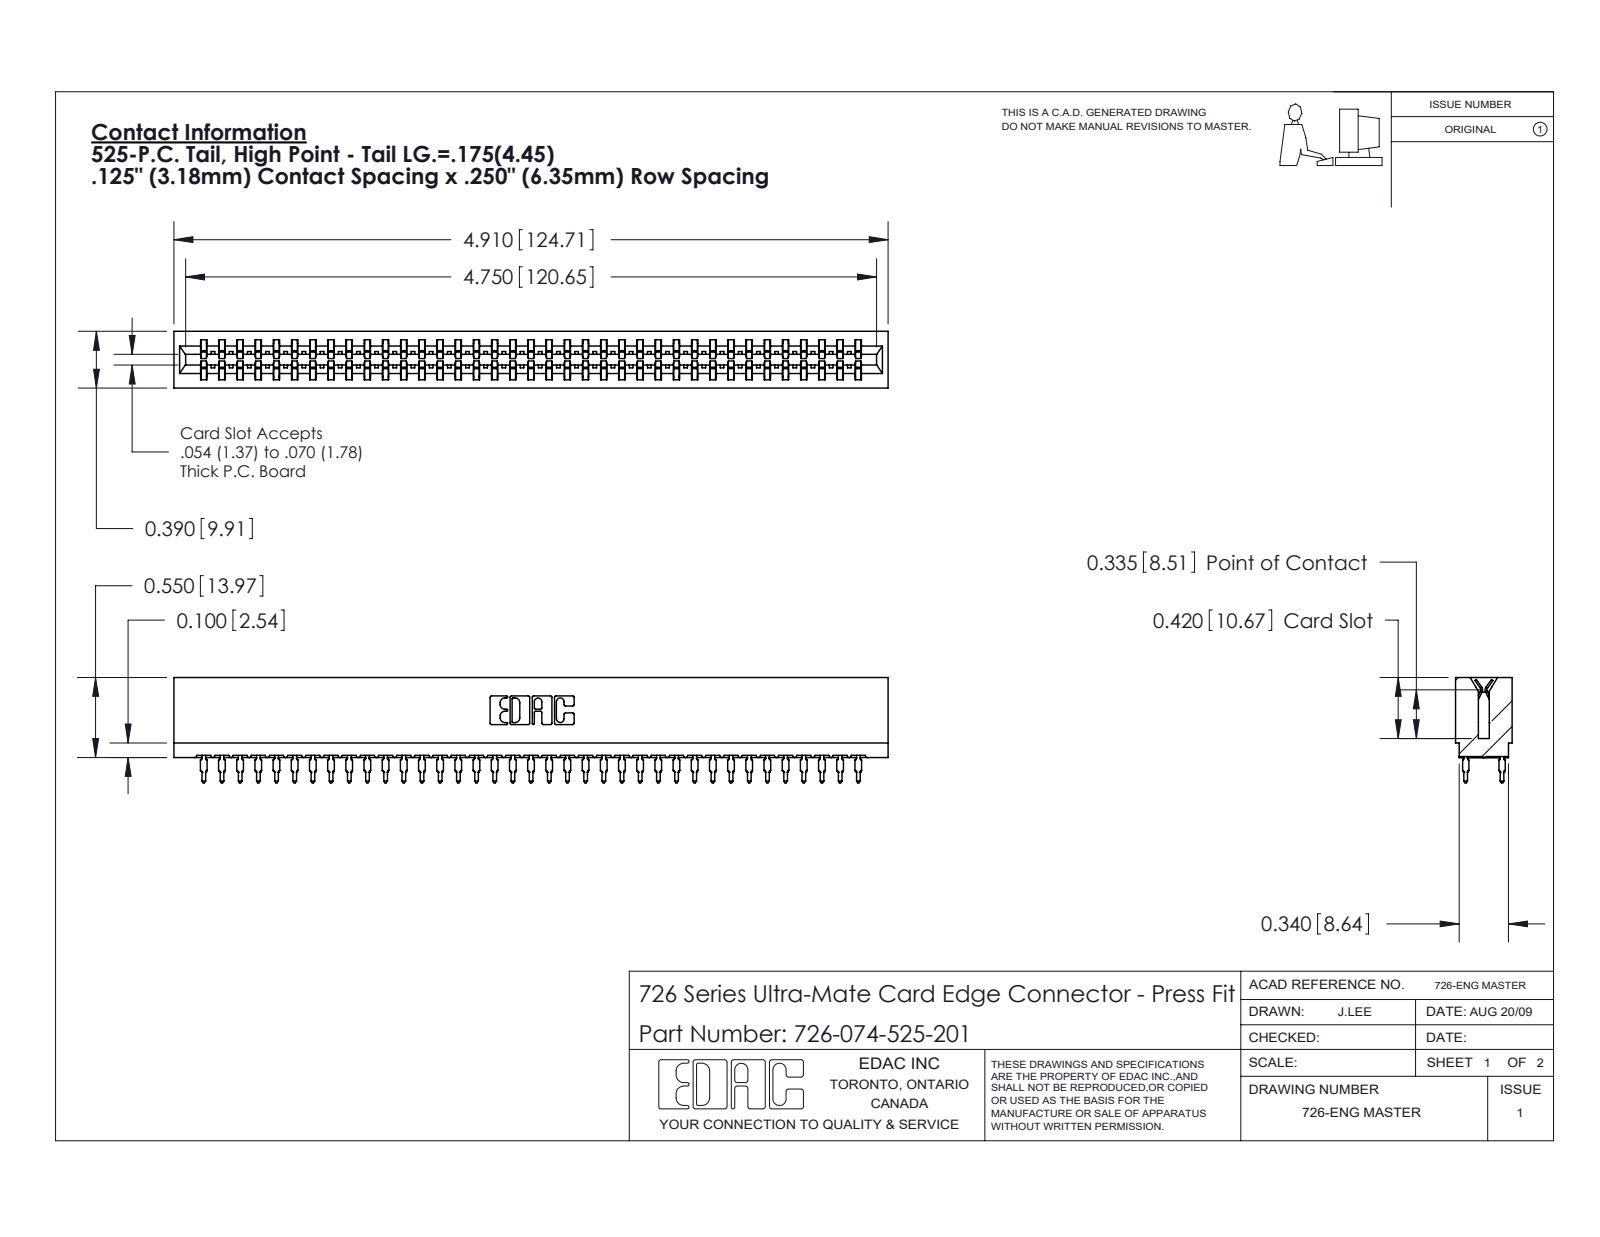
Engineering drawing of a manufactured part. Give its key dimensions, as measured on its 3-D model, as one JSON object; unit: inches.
{"part_name": "746-292-001_525; 726 Part_.515 Slot Depth - 01; 726-074-525-201", "step_written_by": "SolidWorks 2020 (CONFIG_CONTROL_DESIGN)", "units": "inches", "bodies": {"solids": 75, "faces": 6720, "planar": 3459, "cylindrical": 1337, "other": 1924}, "overall_size": [4.91, 0.724, 0.39], "volume_in3": 0.7, "surface_area_in2": 29.22, "partial_cylinders_radius": [[0.021, 148], [0.015, 38], [0.01, 22], [0.005, 8], [0.011, 8], [0.007, 6], [0.031, 6], [0.026, 3]], "face_to_face_distances": [0.057, 0.333, 0.39, 0.25, 0.025, 0.307, 0.275, 0.083, 0.5, 0.365]}
